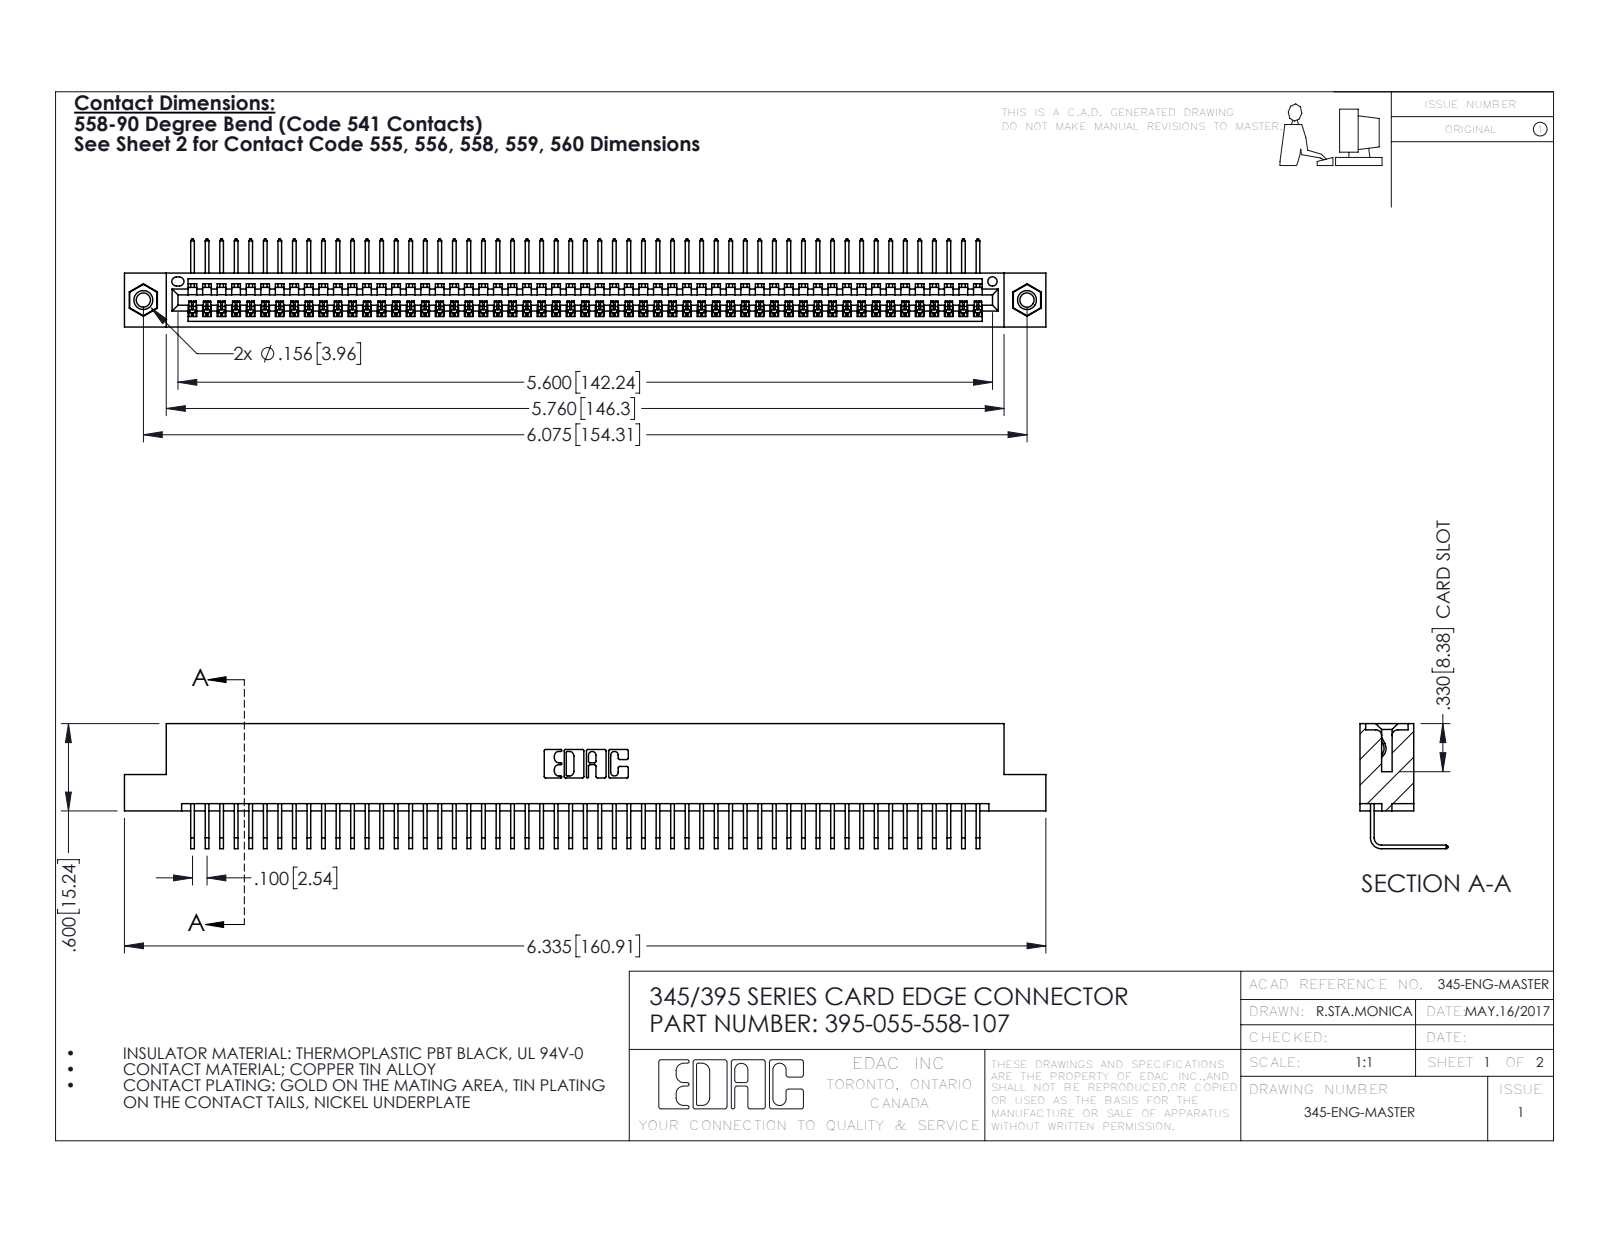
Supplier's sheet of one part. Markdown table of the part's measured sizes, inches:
| quantity | value |
| --- | --- |
| part name | 345-292-001_558 Tail - 2; 395-055-558-107; 345 Part_Flush Mounting Lugs - 0.156 Dia-TI; 345-250-001_345-250-005-103 |
| STEP written by | SolidWorks 2016 (CONFIG_CONTROL_DESIGN) |
| units | inches |
| bodies | 58 solids, 3486 faces (2422 planar, 1048 cylindrical, 16 other) |
| overall size | 6.335 × 0.859 × 0.605 |
| volume | 0.95 in³ |
| surface area | 34.04 in² |
| round holes (diameter × count) | 0.098 × 2, 0.125 × 2, 0.156 × 2, 0.064 × 1 |
| round bosses / shafts (diameter × count) | 0.155 × 2 |
| partial cylindrical surfaces (radius × count) | 0.006 × 110, 0.01 × 22, 0.007 × 6, 0.031 × 6, 0.026 × 3, 0.031 × 2, 0.04 × 2, 0.014 × 1 |
| main face-to-face distances | 0.072, 0.298, 0.37, 0.2, 0.098, 0.272, 0.025, 0.225, 0.149, 0.072 |
| hole center spacings | 0.27, 5.839, 6.075 |
